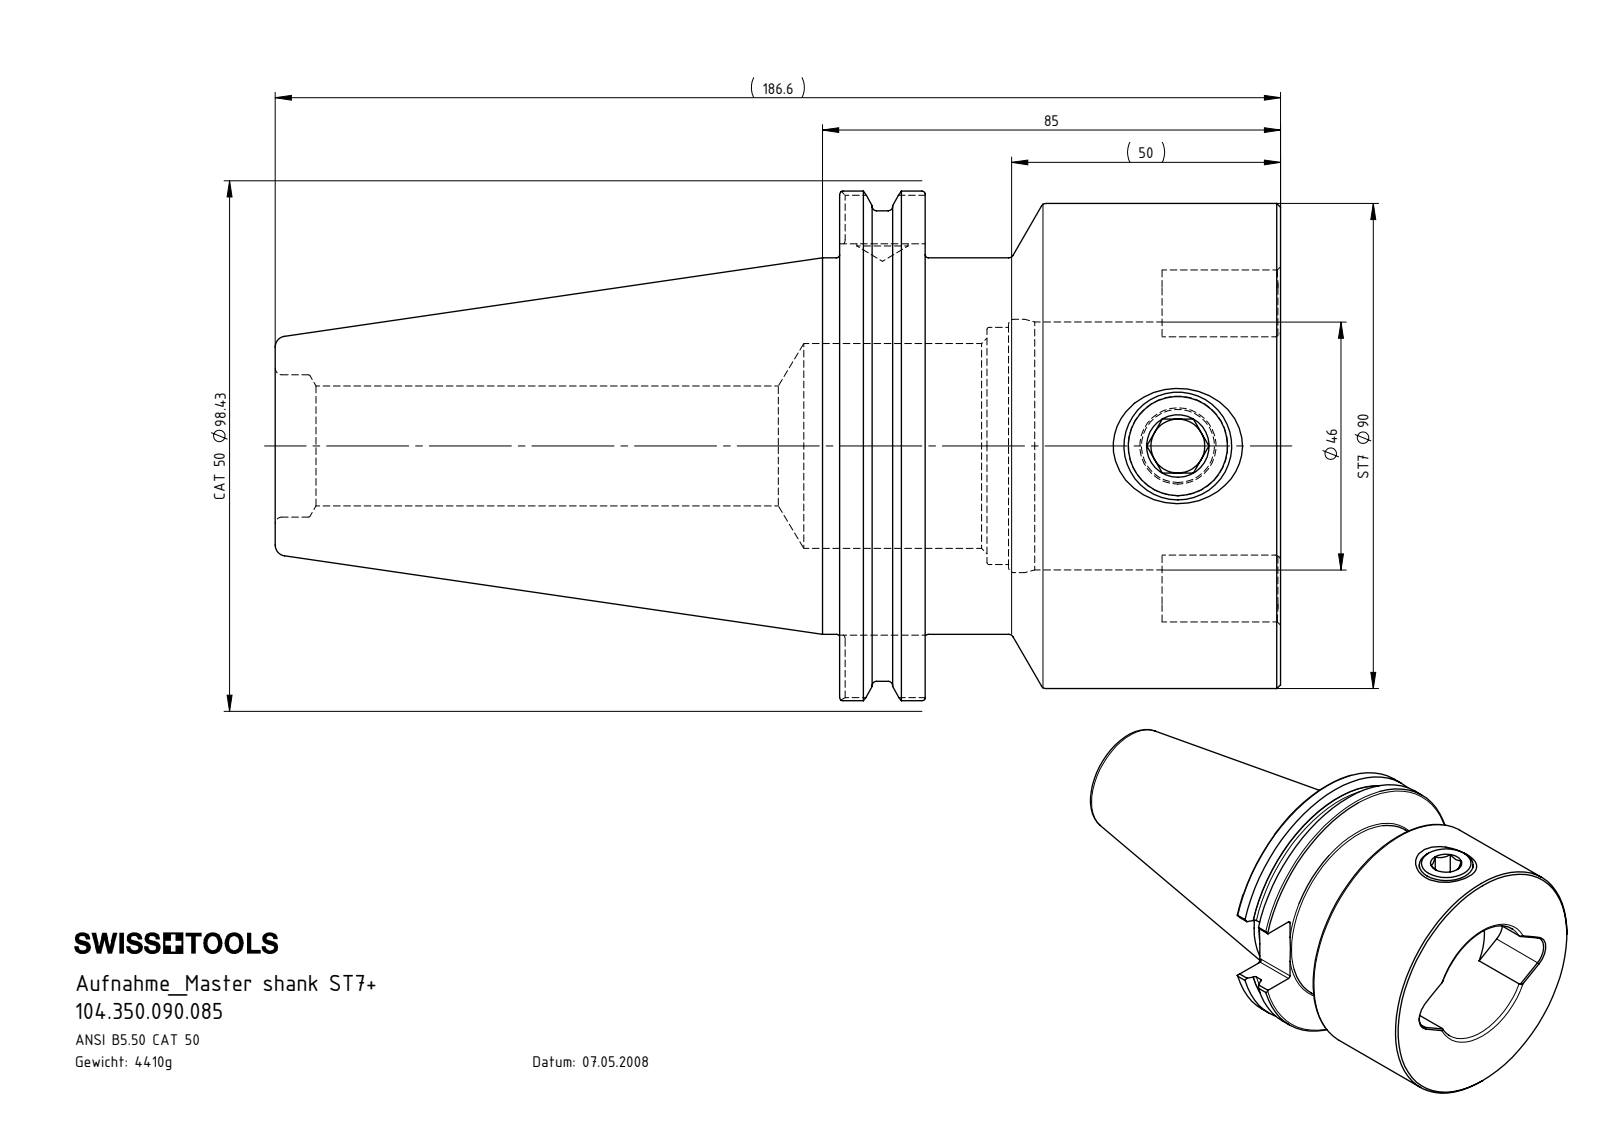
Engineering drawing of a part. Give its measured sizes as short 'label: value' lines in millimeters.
name: ST7-ER1.001.029_A; CT5-ST7.K01.085_A; CT5-ST7.K01.085
written by: SolidWorks 2015 (CONFIG_CONTROL_DESIGN)
unit: mm
bodies: 2 solids, 148 faces (44 planar, 41 cylindrical, 63 other)
size: 186.6 × 98.42 × 94.52
volume: 562 270 mm³; area: 78 672 mm²
holes: 1× ⌀9.5, 1× ⌀18.5, 1× ⌀22.25, 1× ⌀26.4, 1× ⌀38, 1× ⌀44, 1× ⌀46, 1× ⌀47
bosses: 1× ⌀98.42, 1× ⌀91, 1× ⌀90, 1× ⌀69.85, 1× ⌀20
rounds: 8× R0.8, 2× R6.5
face distances: 65.95, 15.87, 81.82, 39.14, 104.78, 120.65, 186.6, 72.6, 164.6, 59.82
